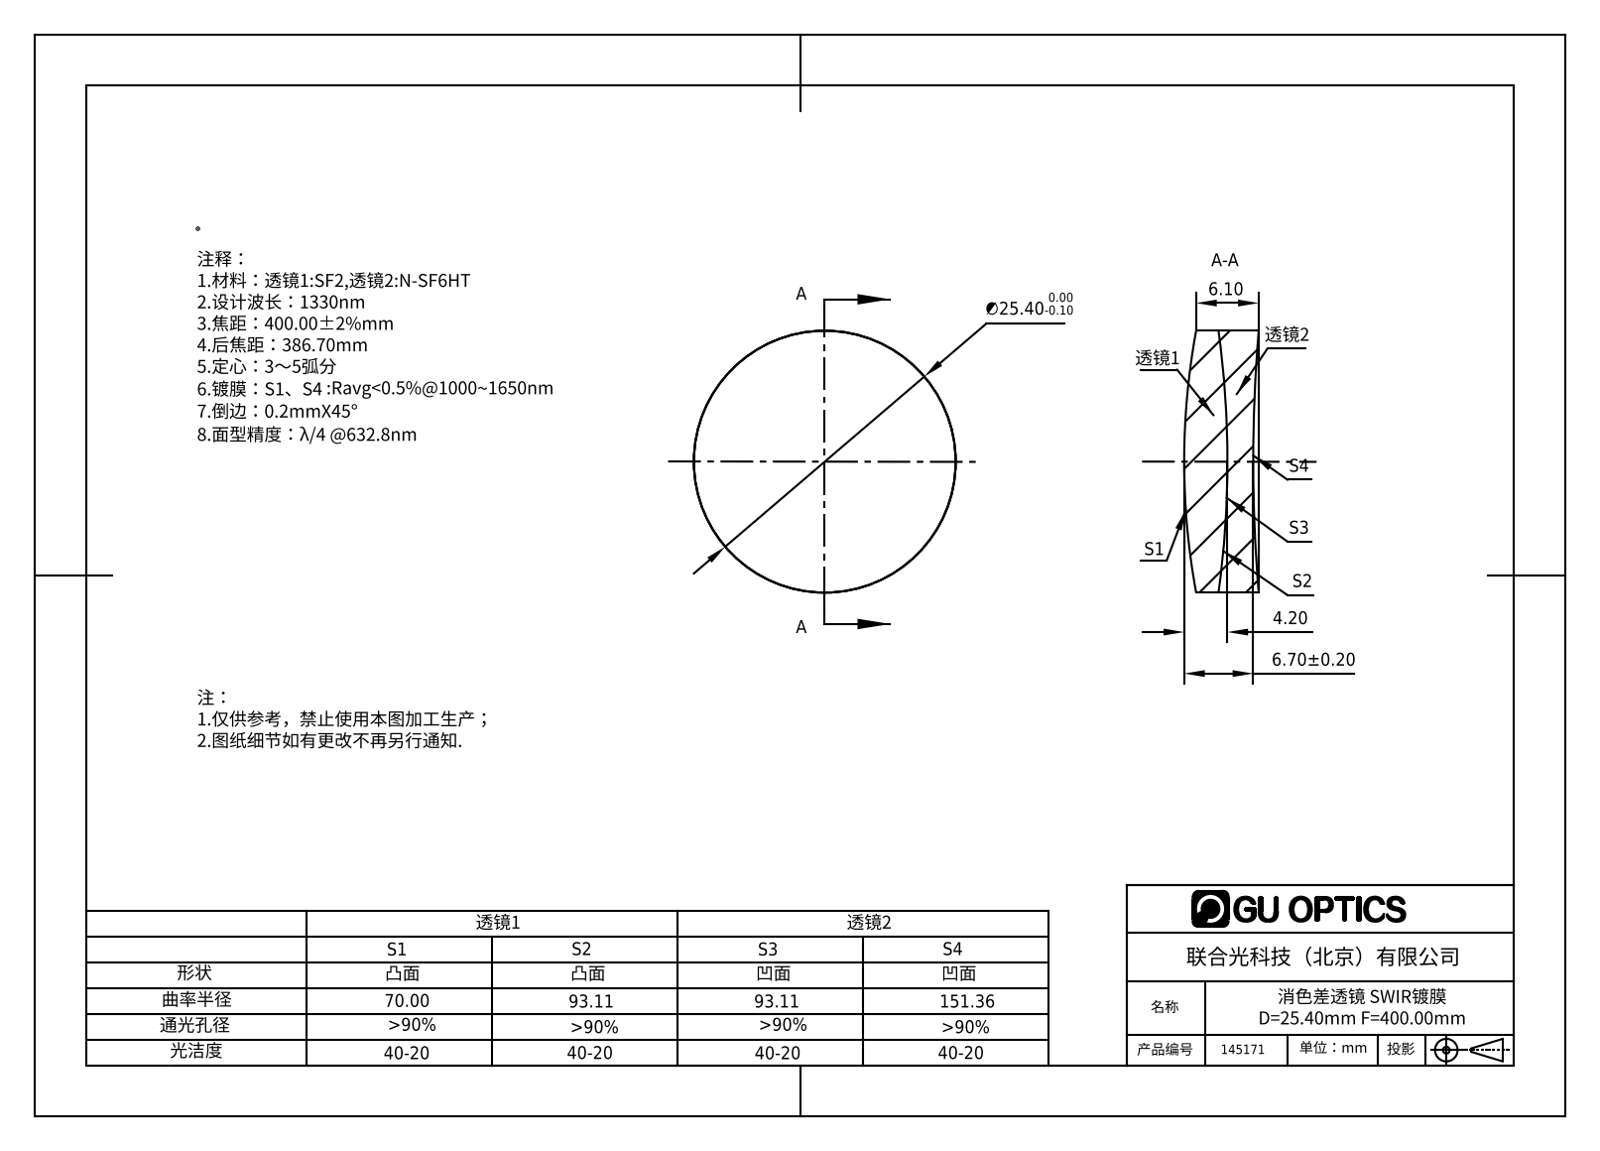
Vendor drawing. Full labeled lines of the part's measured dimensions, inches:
Part name (STEP PRODUCT): 145171
STEP written by: SolidWorks 2016 (AUTOMOTIVE_DESIGN)
Units: inches
Bodies: 2 solids, 12 faces (0 planar, 4 cylindrical, 8 other)
Overall size (bounding box): 1 × 1 × 0.285
Volume: 0.198 in³ · Surface area: 3.908 in²
Round bosses / shafts (diameter × count): ⌀1 ×1
